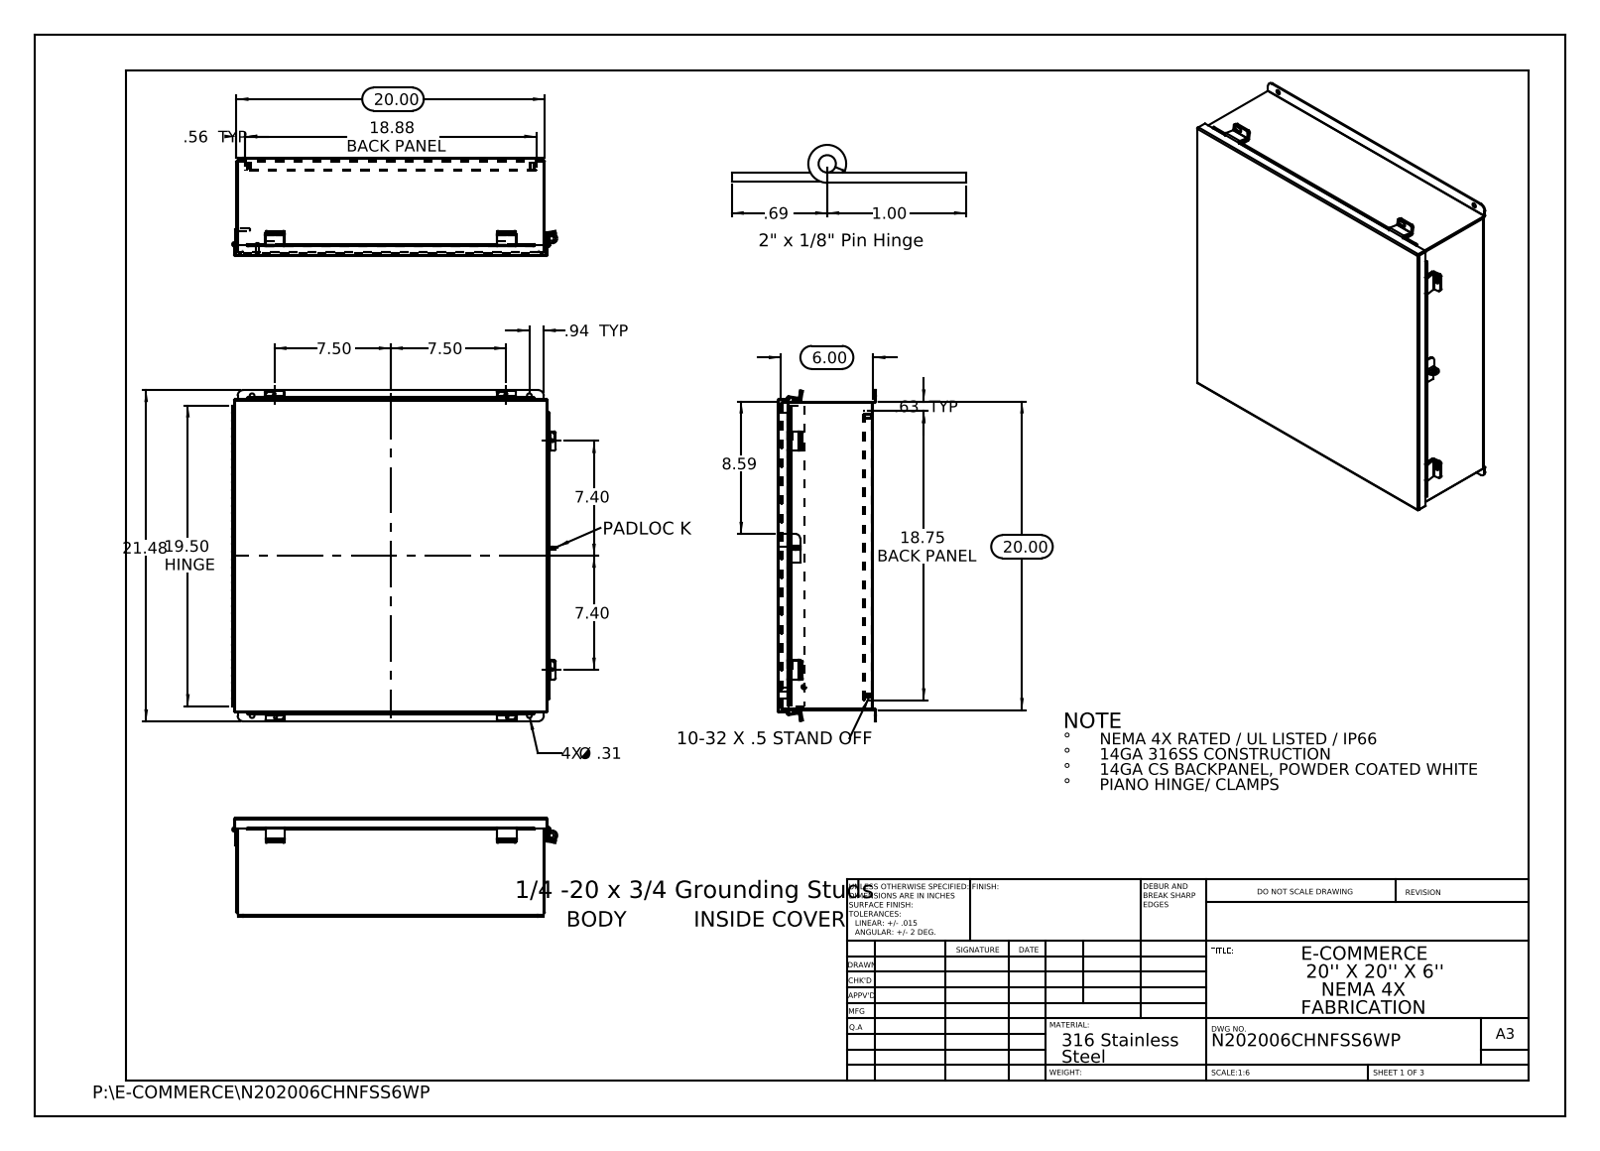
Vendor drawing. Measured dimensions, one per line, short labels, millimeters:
name: N202006CHNFSS6WP JIC_Standoff; N202006CHNFSS6WP Hinge Cover Side JIC; HW-CLH-JH-20104; N202006CHNFSS6WP HW-CD-S-25020-034 (+8 more)
written by: SolidWorks 2013 (CONFIG_CONTROL_DESIGN)
unit: mm
bodies: 27 solids, 938 faces (579 planar, 339 cylindrical, 20 other)
size: 545.5 × 535.2 × 162.3
volume: 2 217 000 mm³; area: 2 367 000 mm²
holes: 10× ⌀6.4, 4× ⌀4.7, 4× ⌀7.9, 1× ⌀3.2, 1× ⌀3.2, 1× ⌀9.5, 1× ⌀9.5
bosses: 4× ⌀8, 2× ⌀8, 2× ⌀6, 1× ⌀6.9, 1× ⌀6.4
rounds: 21× R3.2, 13× R0.3, 12× R0.2, 12× R2.2, 12× R3.4, 6× R2.1, 6× R2.5, 4× R9.5
face distances: 1.9, 155.7, 506.1, 153.7, 157.6, 1.9, 143, 14.6, 12.7, 141
hole spacings: 33.4, 462.8, 493.4, 675.7, 381, 456.6, 460.4, 466.7
